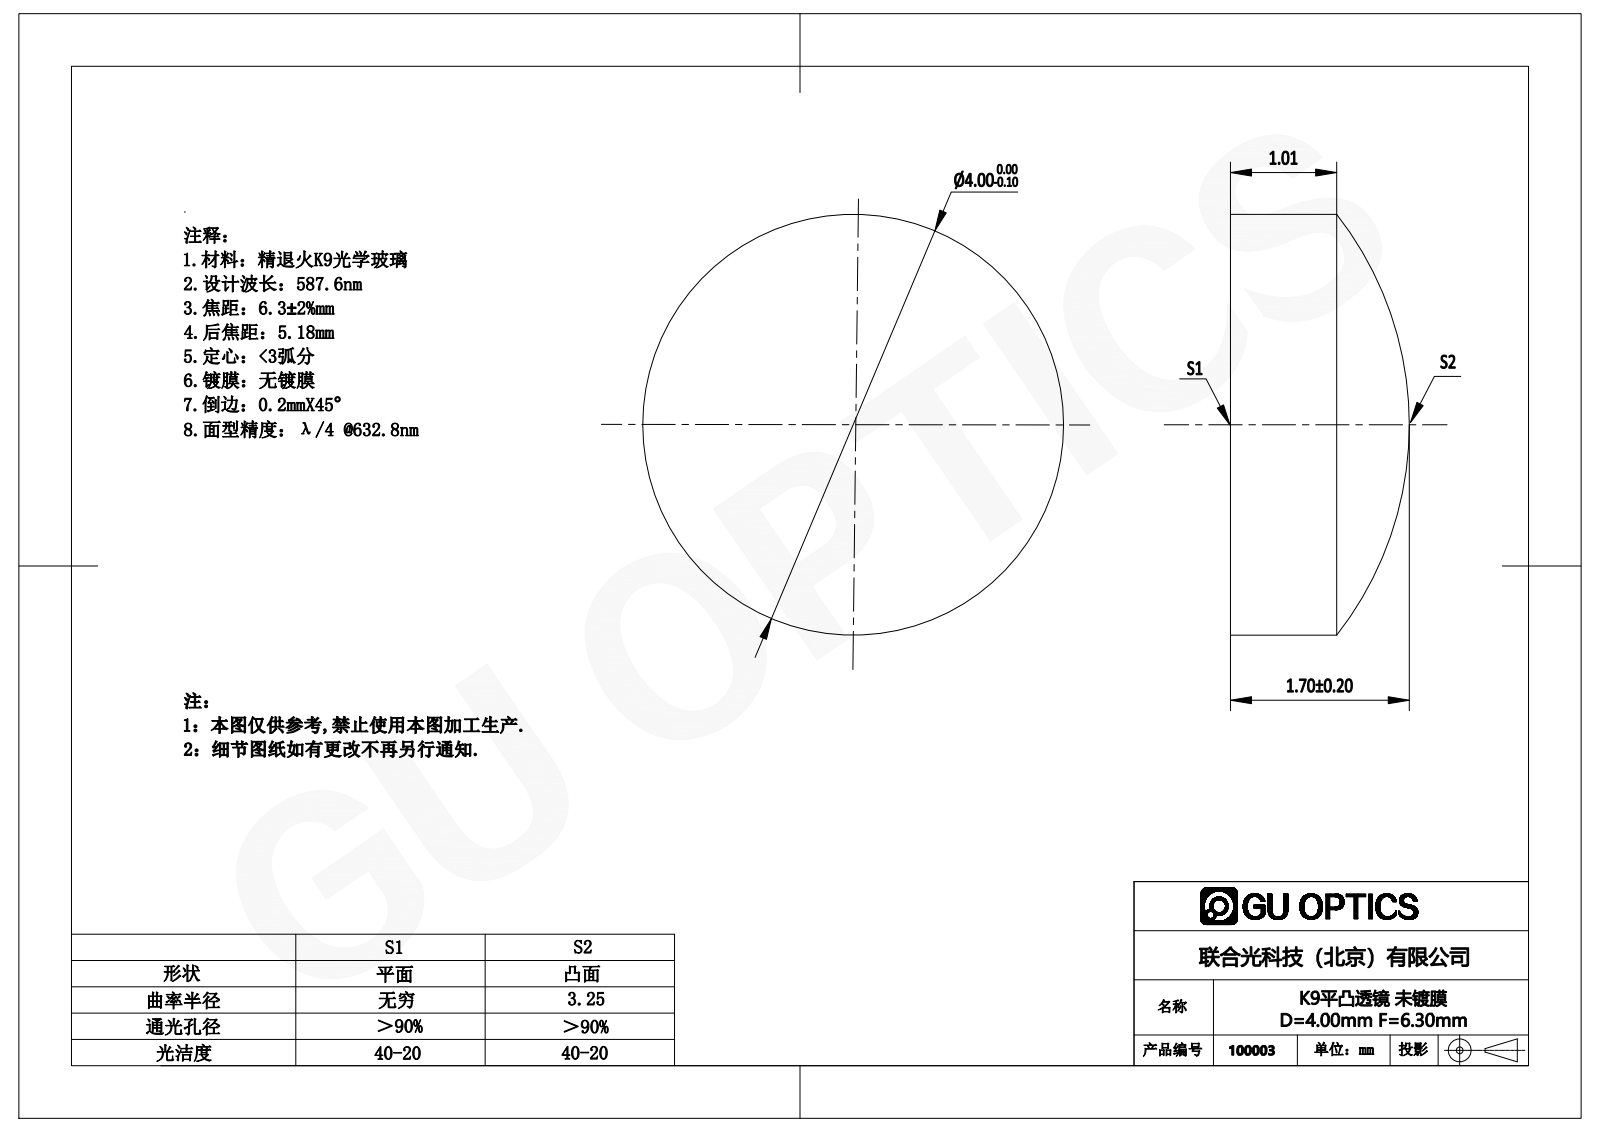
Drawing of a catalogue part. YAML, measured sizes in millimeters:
part_name: "100003"
step_written_by: "SolidWorks 2016 (AUTOMOTIVE_DESIGN)"
units: millimeters
bodies: {solids: 1, faces: 5, planar: 1, cylindrical: 2, other: 2}
overall_size: [4, 4, 1.7]
volume: 17
surface_area: 39
round_bosses_or_shafts:
  - {diameter: 4, count: 1}
